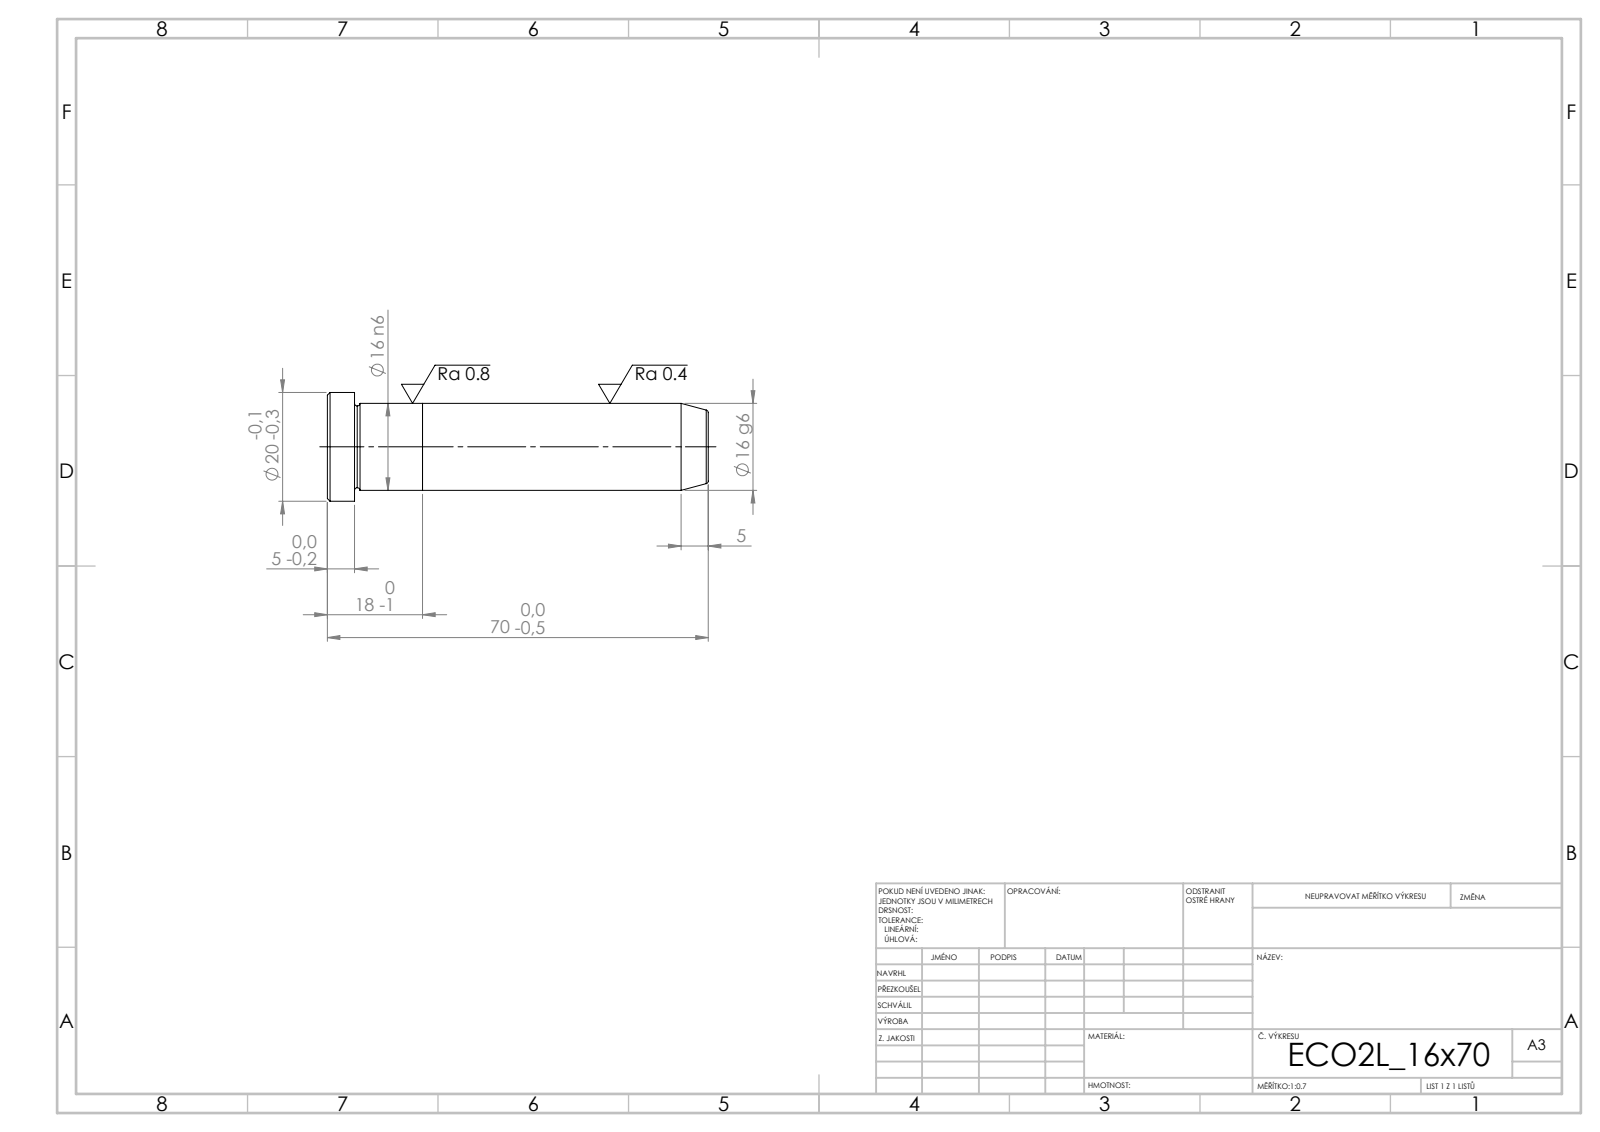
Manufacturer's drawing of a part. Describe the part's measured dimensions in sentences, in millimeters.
Its 3-D file was written by "SolidWorks 2019 (CONFIG_CONTROL_DESIGN)". It is 2 solids with 21 faces: 5 planar, 6 cylindrical and 10 other. Overall it measures 70 by 20 by 20 millimeters. Its volume is 14 453 cubic millimeters and its surface area 4 539 square millimeters. Round bosses or shafts: 1 of diameter 20, 1 of diameter 16. The main face-to-face distances are 17.5, 52.5, 70, 65, 12.5, 5.
